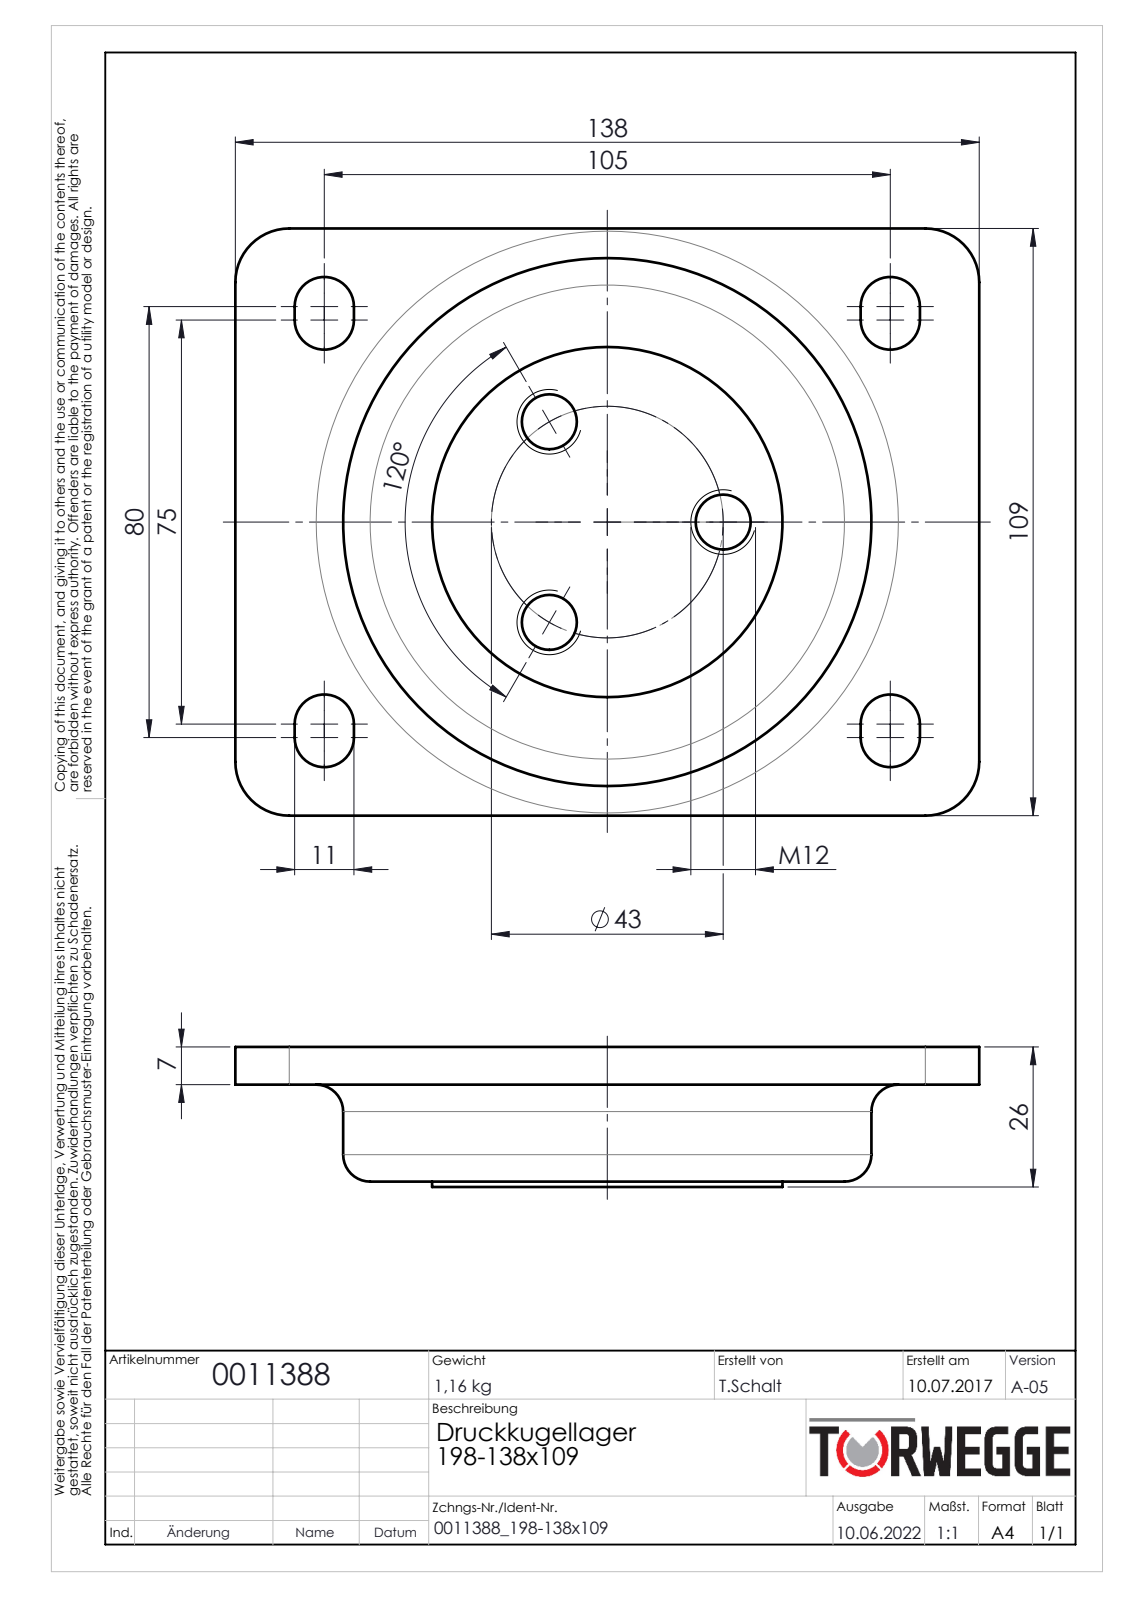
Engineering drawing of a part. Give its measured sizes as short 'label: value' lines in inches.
name: 0011388
written by: SolidWorks 2018 (AUTOMOTIVE_DESIGN)
unit: in
bodies: 1 solid, 52 faces (16 planar, 26 cylindrical, 10 other)
size: 5.433 × 4.291 × 1.024
volume: 14.44 in³; area: 60.85 in²
holes: 3× ⌀0.402
bosses: 1× ⌀3.858, 1× ⌀2.559
rounds: 8× R0.217, 4× R0.394
face distances: 0.276, 1.024, 0.748, 0.984, 0.709, 0.039, 4.291, 5.433, 0.433, 4.567
hole spacings: 1.466
